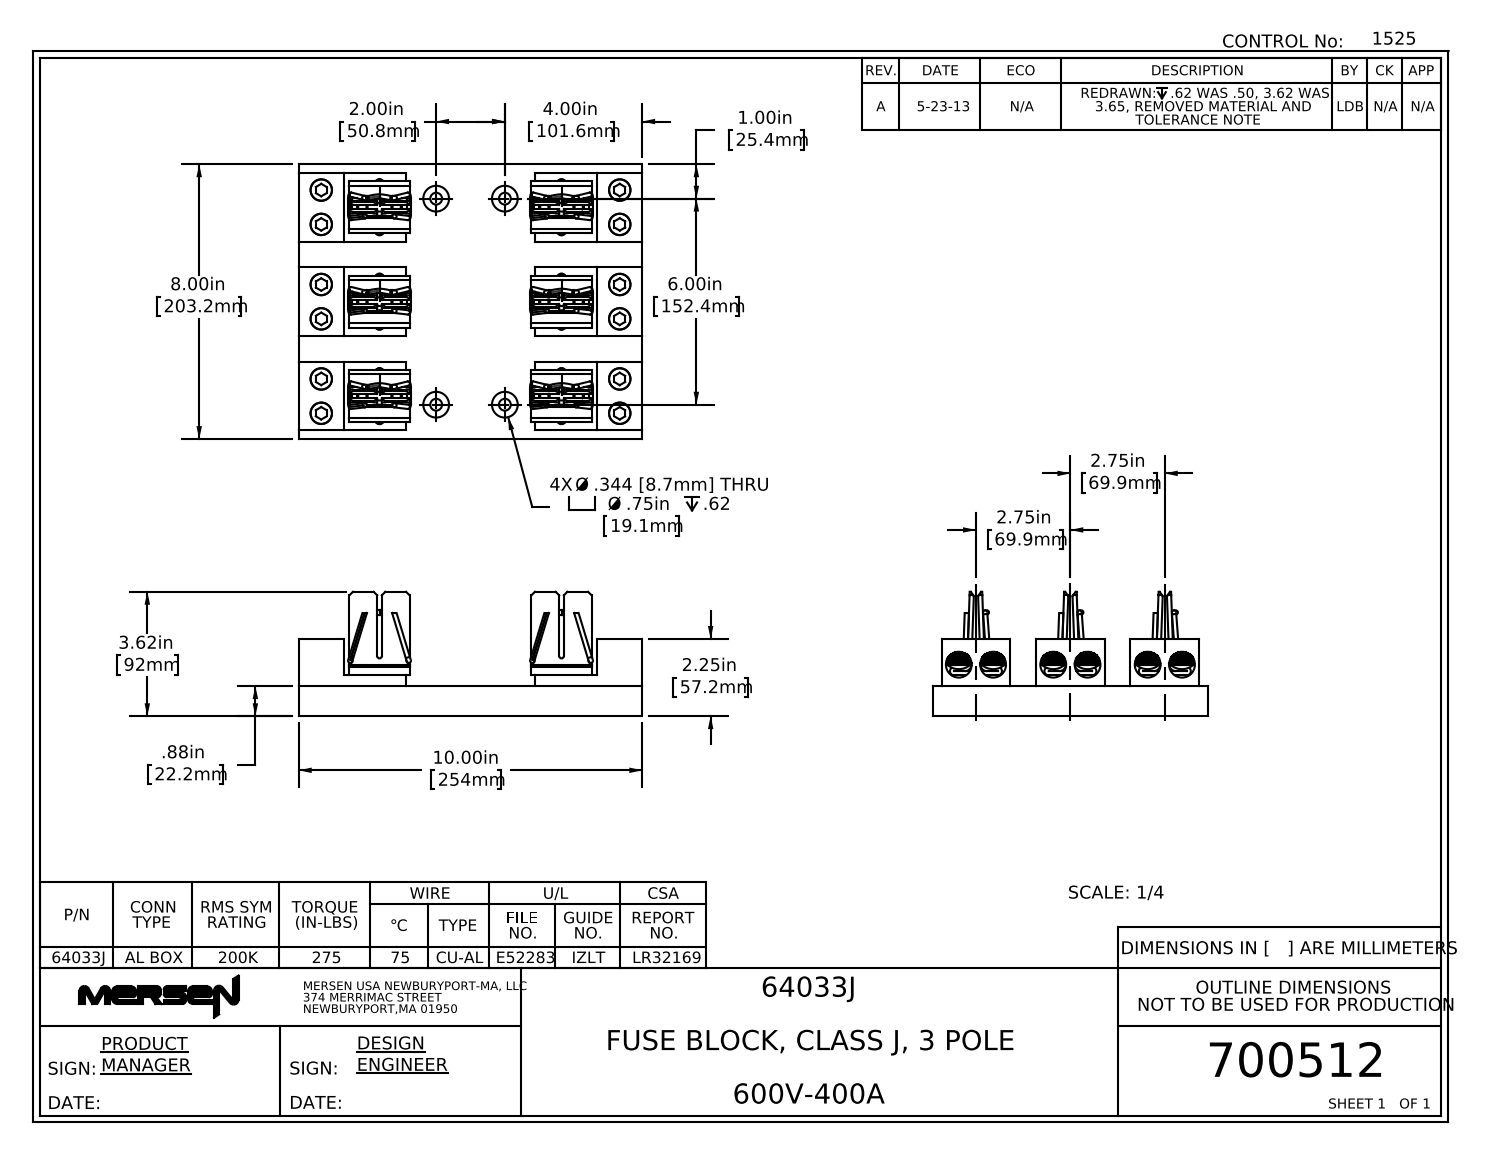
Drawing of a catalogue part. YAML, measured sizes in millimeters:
part_name: "700512reva"
step_written_by: "SolidWorks 2012 (AUTOMOTIVE_DESIGN)"
units: millimeters
bodies: {solids: 55, faces: 2078, planar: 658, cylindrical: 364, other: 1056}
overall_size: [254.1, 203.2, 92]
volume: 1611000
surface_area: 412100
round_holes:
  - {diameter: 6.5, count: 24}
  - {diameter: 15.9, count: 18}
  - {diameter: 8.6, count: 12}
  - {diameter: 21.6, count: 12}
  - {diameter: 19.1, count: 10}
  - {diameter: 8, count: 6}
  - {diameter: 9.6, count: 6}
  - {diameter: 15.9, count: 6}
  - {diameter: 8.7, count: 4}
round_bosses_or_shafts:
  - {diameter: 8, count: 24}
partial_cylinders:
  - {radius: 1.6, count: 6}
  - {radius: 3.2, count: 6}
  - {radius: 4.7, count: 6}
  - {radius: 2.4, count: 4}
  - {radius: 1.8, count: 2}
face_to_face_distances: [22.2, 3.1, 69.8, 30.1, 7.9, 139.5, 72.9, 66.6, 57.2, 6.4]
hole_center_spacings: [21.6, 69.9, 53.9, 88.2, 151.7, 123.2, 134.6, 148.4]
